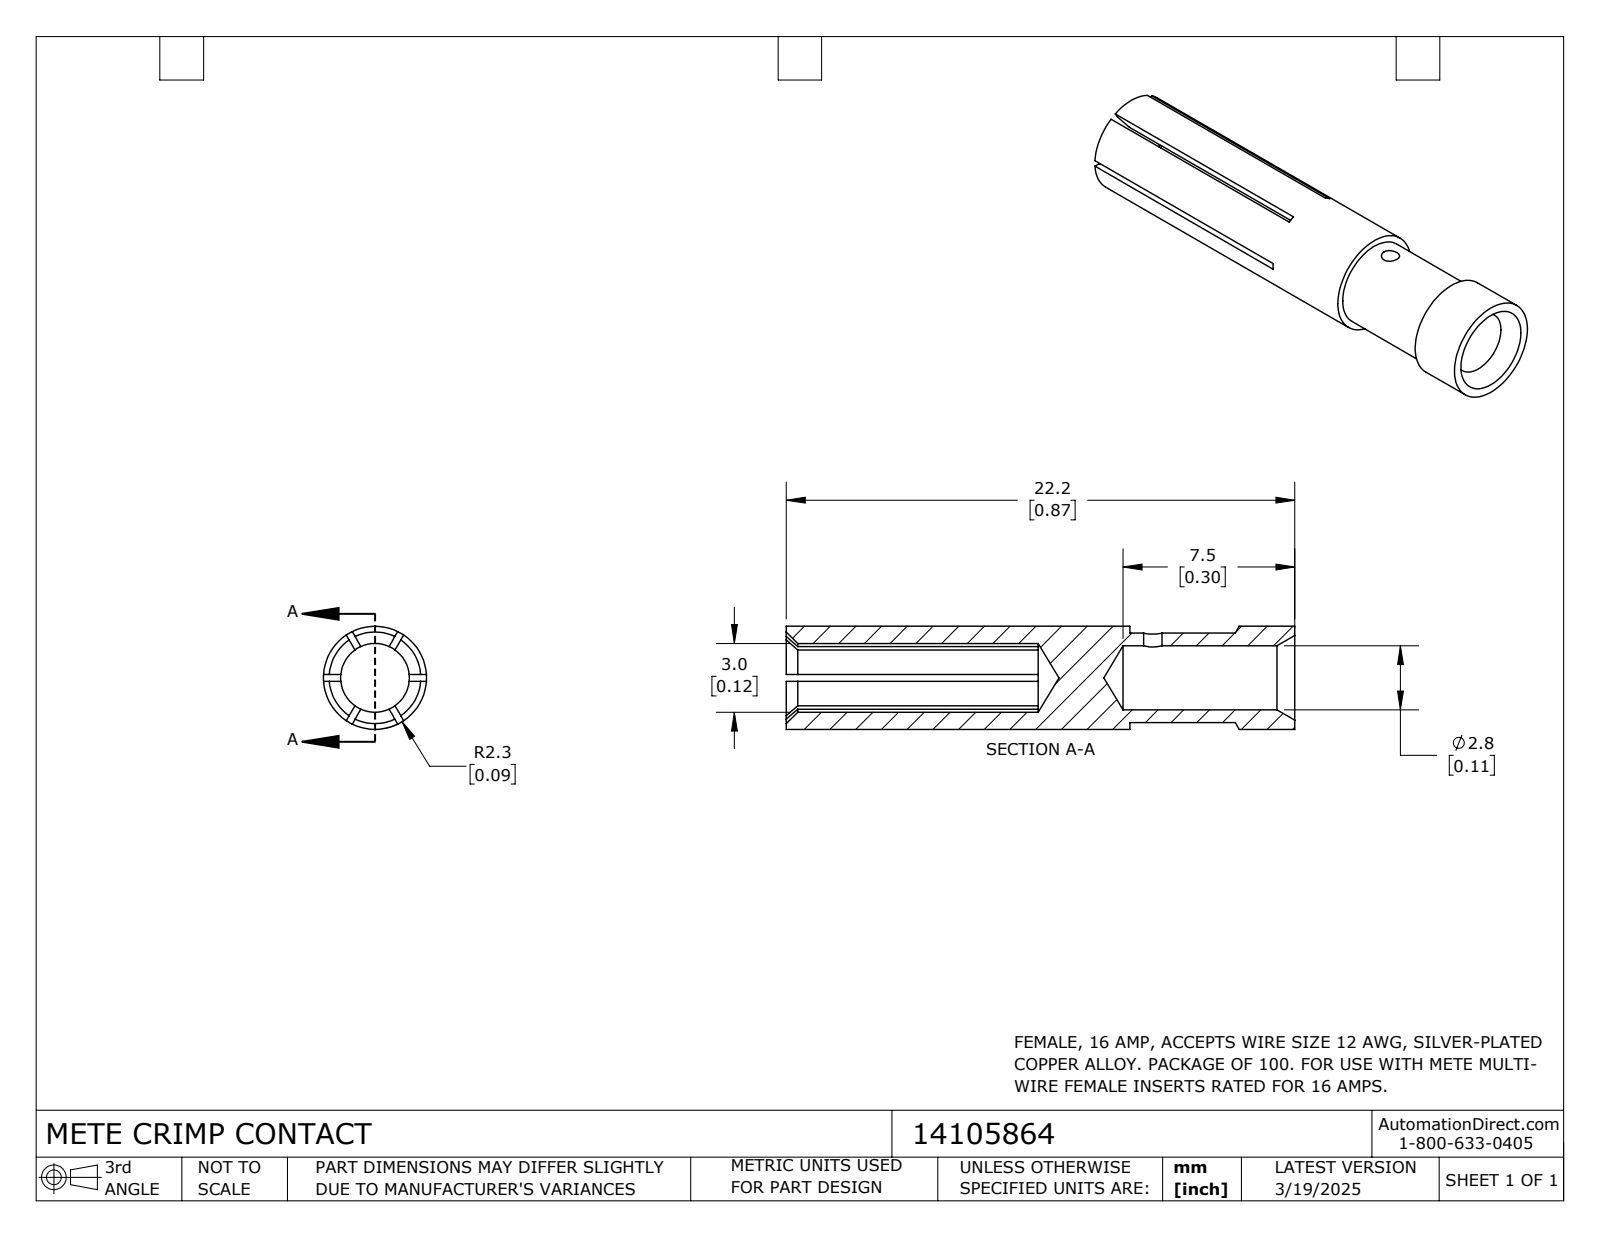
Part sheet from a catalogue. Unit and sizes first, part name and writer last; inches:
Units: inches
Overall size (bounding box): 0.874 × 0.177 × 0.177
Round holes (diameter × count): ⌀0.031 ×1, ⌀0.11 ×1, ⌀0.118 ×1
Round bosses / shafts (diameter × count): ⌀0.177 ×1, ⌀0.154 ×1
Main face-to-face distances: 0.283, 0.874, 0.591, 0.441, 0.157, 0.433
Volume: 0.012 in³ · Surface area: 0.882 in²
Bodies: 1 solid, 56 faces (26 planar, 16 cylindrical, 14 other)
Part name (STEP PRODUCT): 14105864
STEP written by: SolidWorks 2024 (CONFIG_CONTROL_DESIGN)
